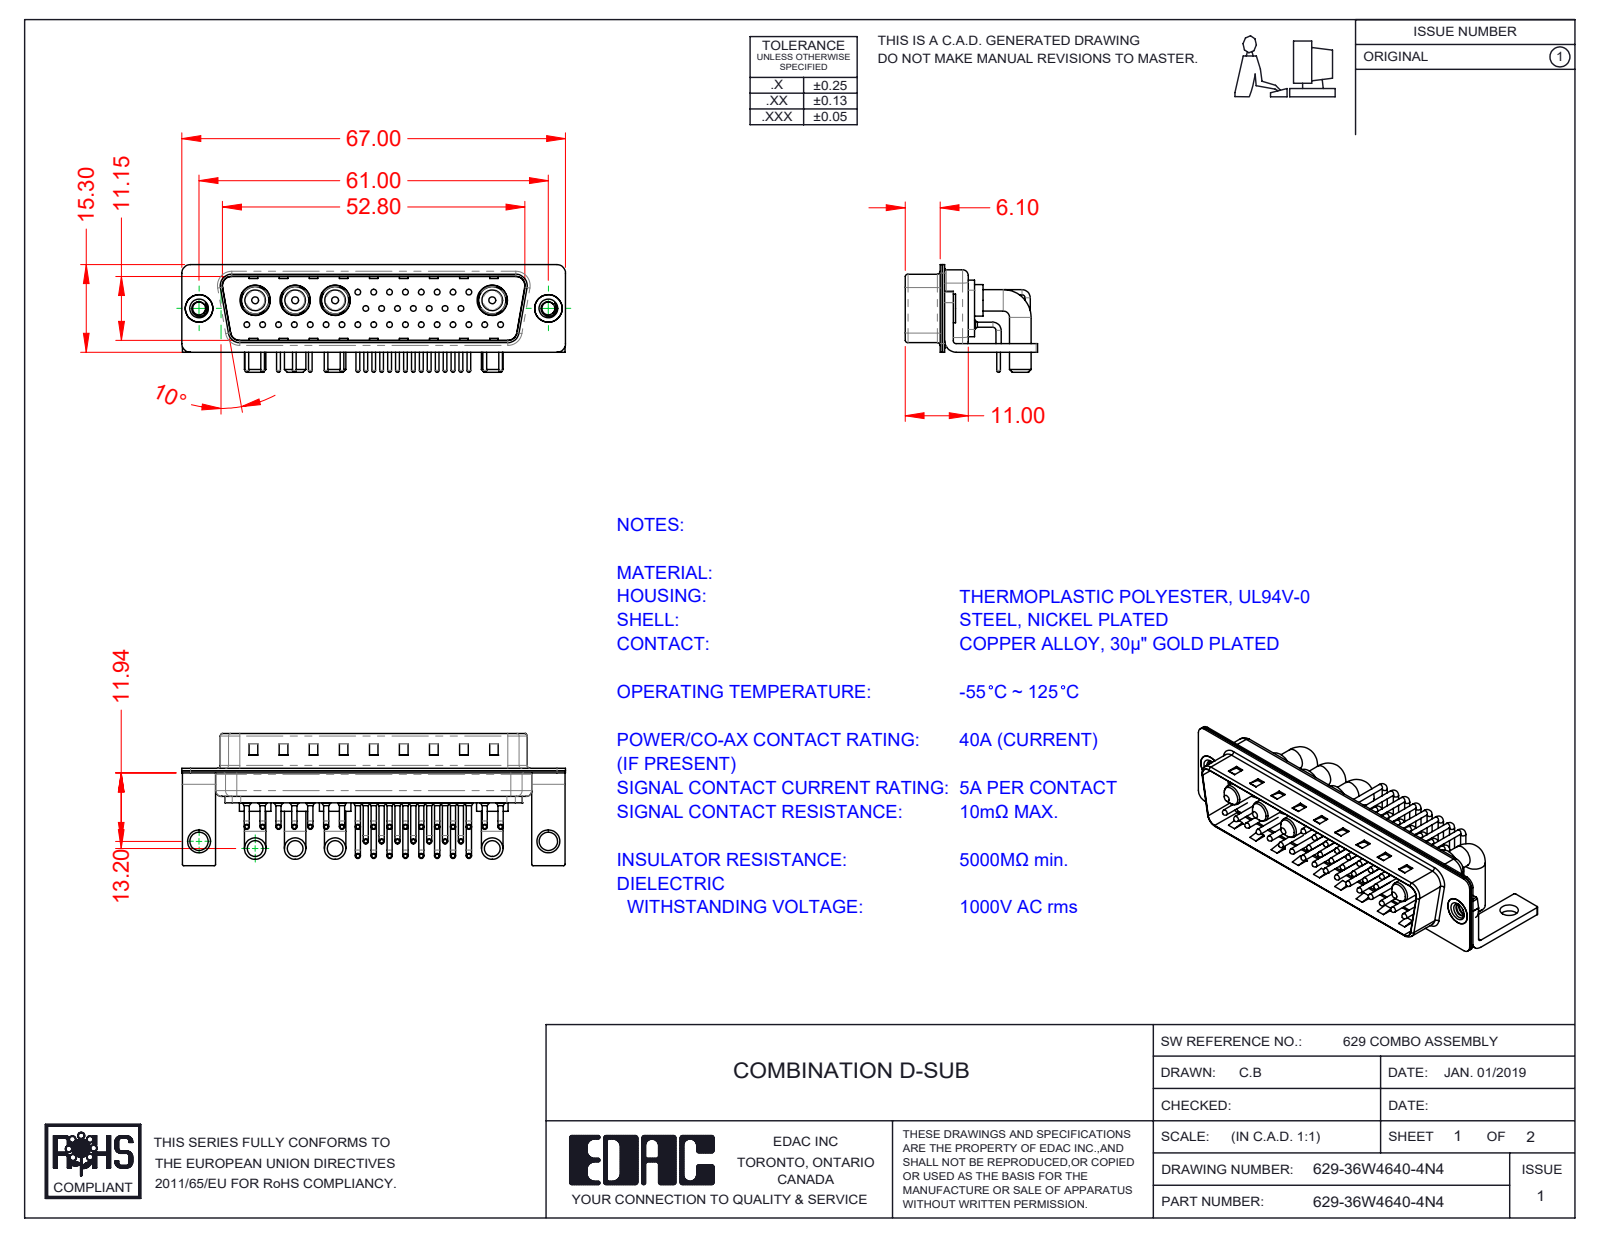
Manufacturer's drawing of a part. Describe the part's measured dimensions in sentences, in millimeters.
The part is named "629Combo Housing_36W4; 629Combo Contact Row 3; 629Combo Contact Row 2_50 Contacts; 629-36W4640-4N4 (+6 more)". Its 3-D file was written by "SolidWorks 2020 (CONFIG_CONTROL_DESIGN)". It is 47 solids with 4144 faces: 2311 planar, 1395 cylindrical and 438 other. Overall it measures 67 by 23.1 by 18.8 millimeters. Its volume is 6 103 cubic millimeters and its surface area 13 308 square millimeters. Round holes: 32 of diameter 0.75, 32 of diameter 1.6, 32 of diameter 2, 4 of diameter 4.85, 4 of diameter 5.3, 2 of diameter 2.26, 2 of diameter 3.2, 2 of diameter 4, 2 of diameter 4.8. Round bosses or shafts: 64 of diameter 0.9, 32 of diameter 1.5, 32 of diameter 1, 32 of diameter 0.65, 8 of diameter 3.75, 4 of diameter 5.5, 4 of diameter 5.2, 4 of diameter 4.75. Partial cylindrical surfaces (rounded edges, fillets, slot ends): 32 of radius 1.01, 16 of radius 0.25, 16 of radius 1.5, 13 of radius 2, 9 of radius 0.5, 8 of radius 1.6, 4 of radius 0.6, 4 of radius 0.65. The main face-to-face distances are 0.4, 1.5, 11.55, 5.6, 5.2, 0.8, 6, 1.9, 0.78, 1.1. The hole center spacings are 2.77, 5.54, 3.16, 8.31, 11.08, 13.85, 16.62, 19.39.
